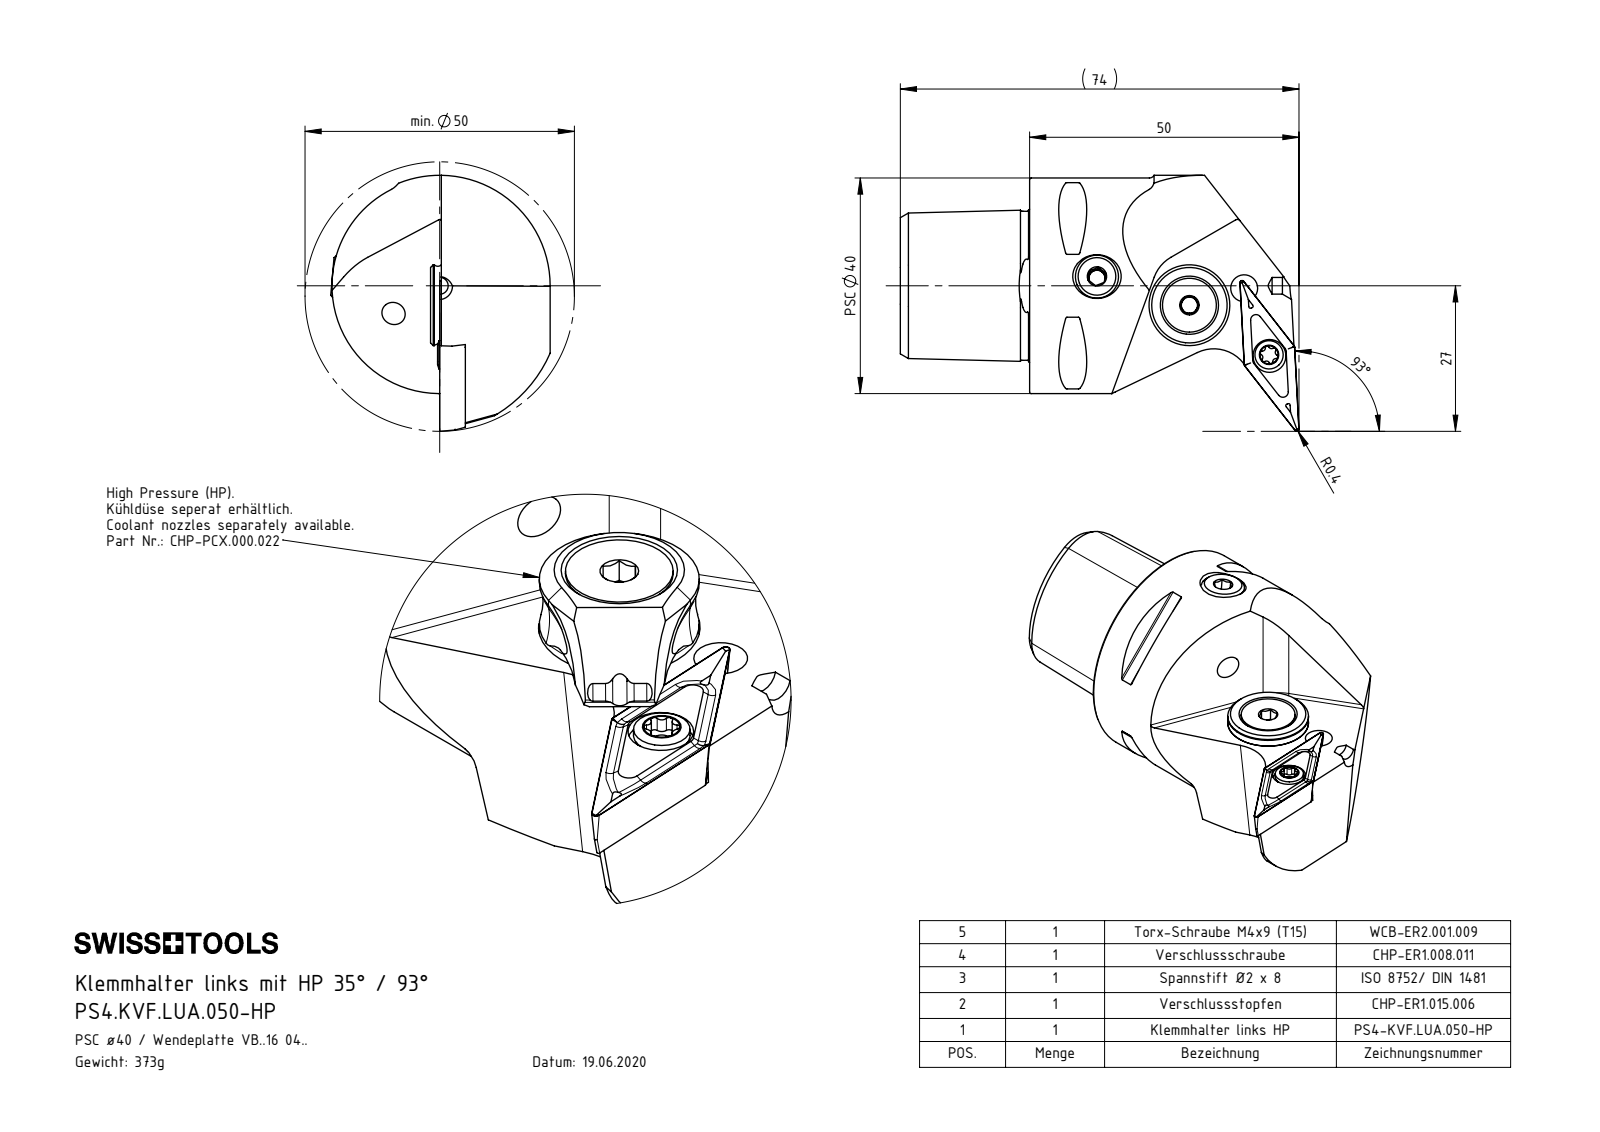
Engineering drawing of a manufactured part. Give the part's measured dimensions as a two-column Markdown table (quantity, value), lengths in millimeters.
| quantity | value |
| --- | --- |
| part name | CHP-ER1.008.011_A; DIN 3771 - 13x1; CHP-ER1.015.006; PS4-KVF.LUA.050-HP_A (+6 more) |
| STEP written by | SolidWorks 2017 (AUTOMOTIVE_DESIGN) |
| units | millimeters |
| bodies | 8 solids, 284 faces (92 planar, 66 cylindrical, 126 other) |
| overall size | 74 × 47.5 × 40.73 |
| volume | 47 368 mm³ |
| surface area | 15 485 mm² |
| round holes (diameter × count) | 3.3 × 2, 4.2 × 2, 5 × 2, 1.2 × 1, 2 × 1, 2.5 × 1, 3 × 1, 4 × 1, 4.4 × 1, 4.6 × 1, 5.2 × 1, 6.1 × 1 |
| round bosses / shafts (diameter × count) | 40 × 1, 15 × 1, 13.4 × 1, 10 × 1, 8 × 1, 5.5 × 1, 5.25 × 1, 5 × 1 |
| partial cylindrical surfaces (radius × count) | 0.3 × 8, 0.34 × 6, 0.59 × 6, 0.15 × 2, 0.5 × 2, 7 × 2, 1.57 × 1, 3 × 1 |
| main face-to-face distances | 20.2, 15.7, 4.5, 15.74, 4.46, 24, 15.52, 35.3, 15, 22.1 |
| hole center spacings | 4.5, 6.74, 10.64, 13.18, 13.4, 13.51, 13.7, 17.41 |
